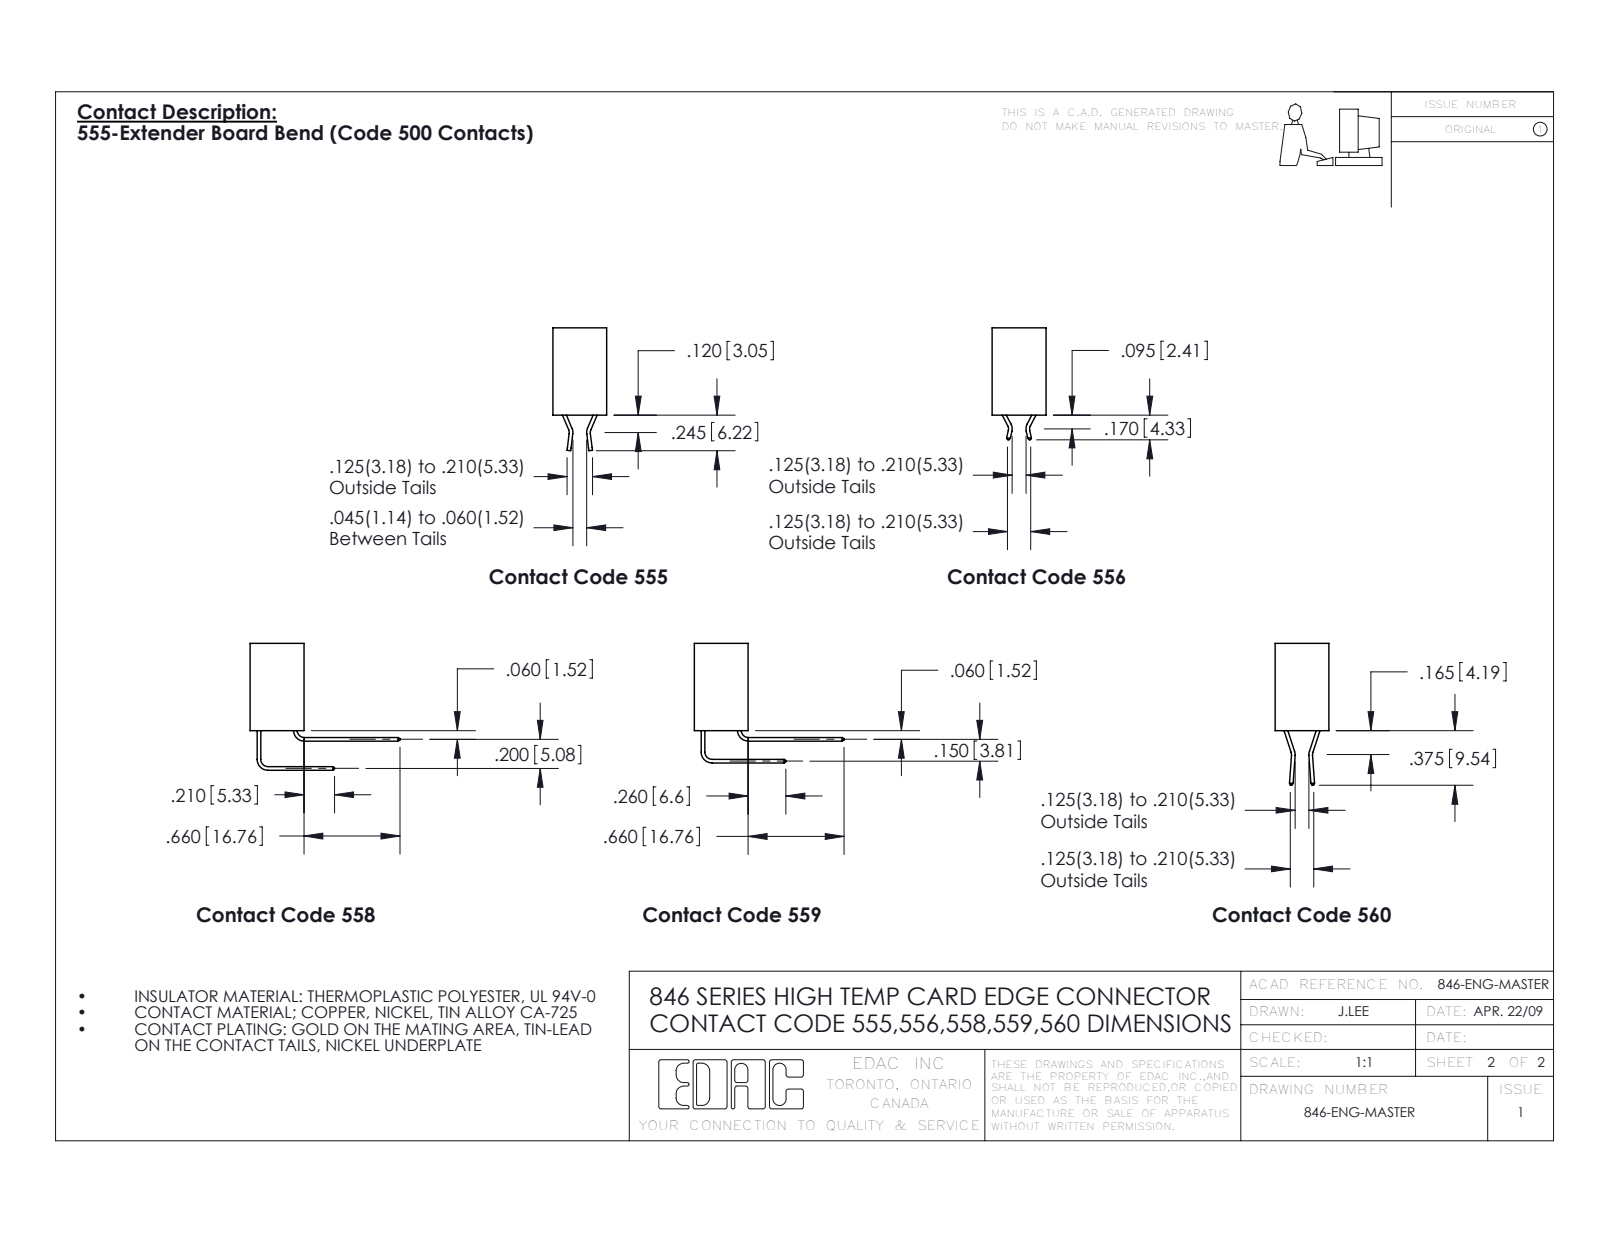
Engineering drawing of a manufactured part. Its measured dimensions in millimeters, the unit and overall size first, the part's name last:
Units: millimetres
Overall size (bounding box): 36.4 × 21.8 × 9.4
Round holes (diameter × count): ⌀2.5 ×2, ⌀3.2 ×2, ⌀4 ×2, ⌀1.6 ×1
Round bosses / shafts (diameter × count): ⌀3.9 ×2
Partial cylindrical surfaces — rounded edges, fillets, slot ends (radius × count): R0.3 ×22, R0.2 ×10, R0.4 ×10, R0.5 ×10, R0.2 ×6, R0.8 ×6, R0.7 ×3, R0.8 ×2
Main face-to-face distances: 6.4, 9.4, 1.2, 8.2, 5.6, 3.8, 2.5, 4.4, 1.8, 7.6
Hole centre spacings: 6.2, 24.6, 29.7
Volume: 3 060 mm³ · Surface area: 3 643 mm²
Bodies: 8 solids, 456 faces (282 planar, 158 cylindrical, 16 other)
Part name (STEP PRODUCT): 896-005-500-607; 345-292-001_345-293-100; 345-250-001_345-250-005-103; 846 Part_0.170 Offset - 0.156 Dia-TI
STEP written by: SolidWorks 2020 (CONFIG_CONTROL_DESIGN)
